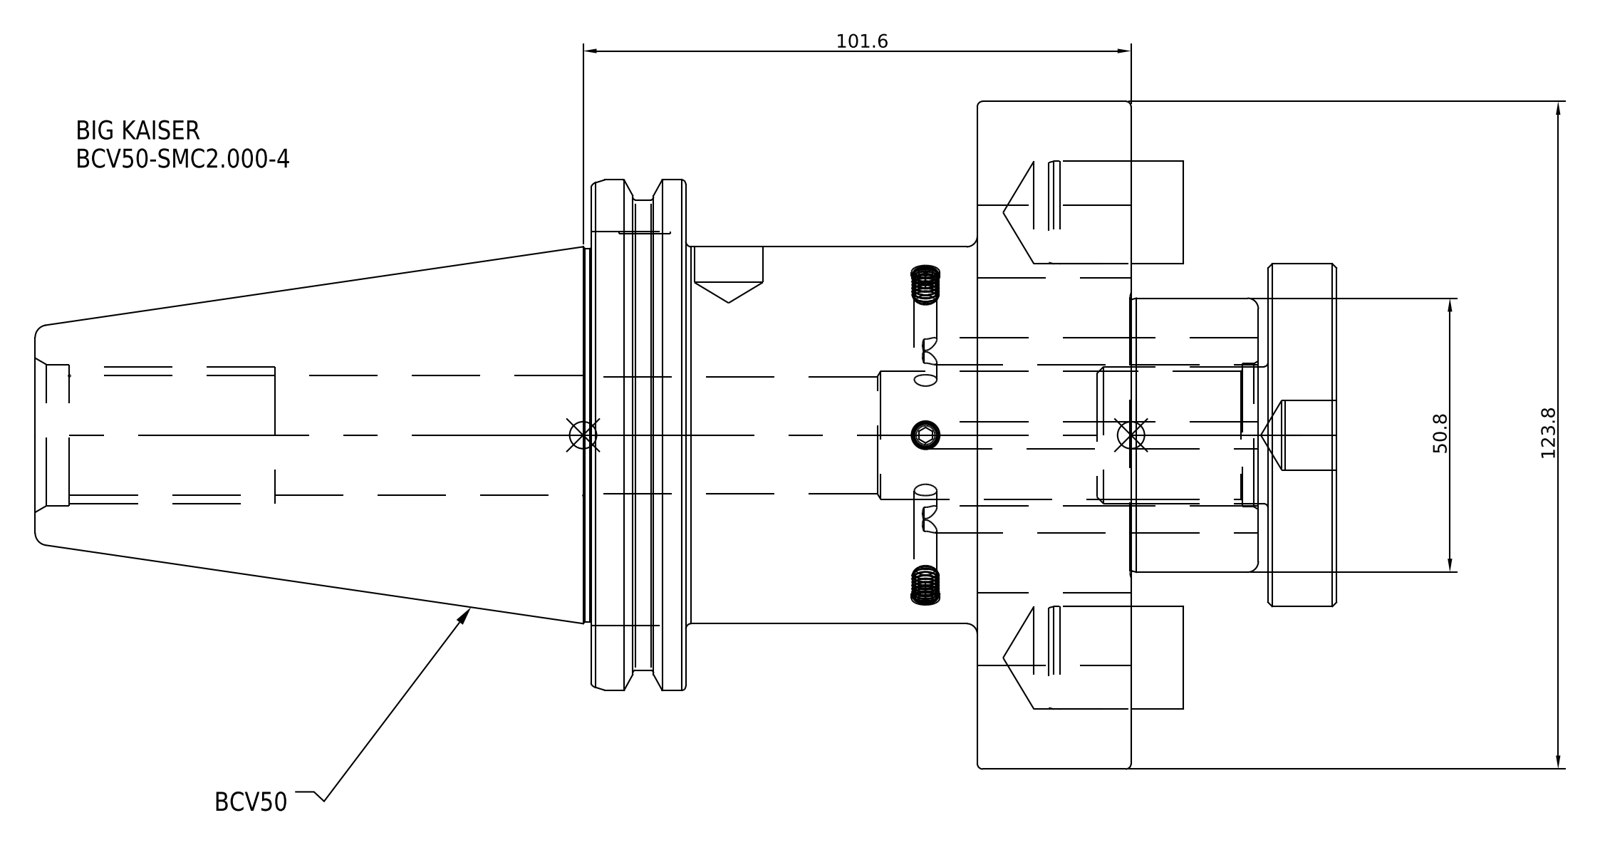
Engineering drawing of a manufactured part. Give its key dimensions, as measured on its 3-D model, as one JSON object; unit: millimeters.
{"part_name": "BCV50-SMC2_000-4", "step_written_by": "SolidWorks 2021 (CONFIG_CONTROL_DESIGN)", "units": "millimeters", "bodies": {"solids": 1, "faces": 38, "planar": 18, "cylindrical": 14, "other": 6}, "overall_size": [212.85, 123.8, 123.8], "volume_mm3": 908949, "surface_area_mm2": 83287, "round_holes": [[23.81, 1]], "round_bosses_or_shafts": [[123.8, 1], [98.43, 1], [91.29, 1], [69.85, 1]], "face_to_face_distances": [28.5, 100.1, 71.6, 82.55, 54.05, 17.55, 203.2, 174.7, 120.65, 103.1]}
